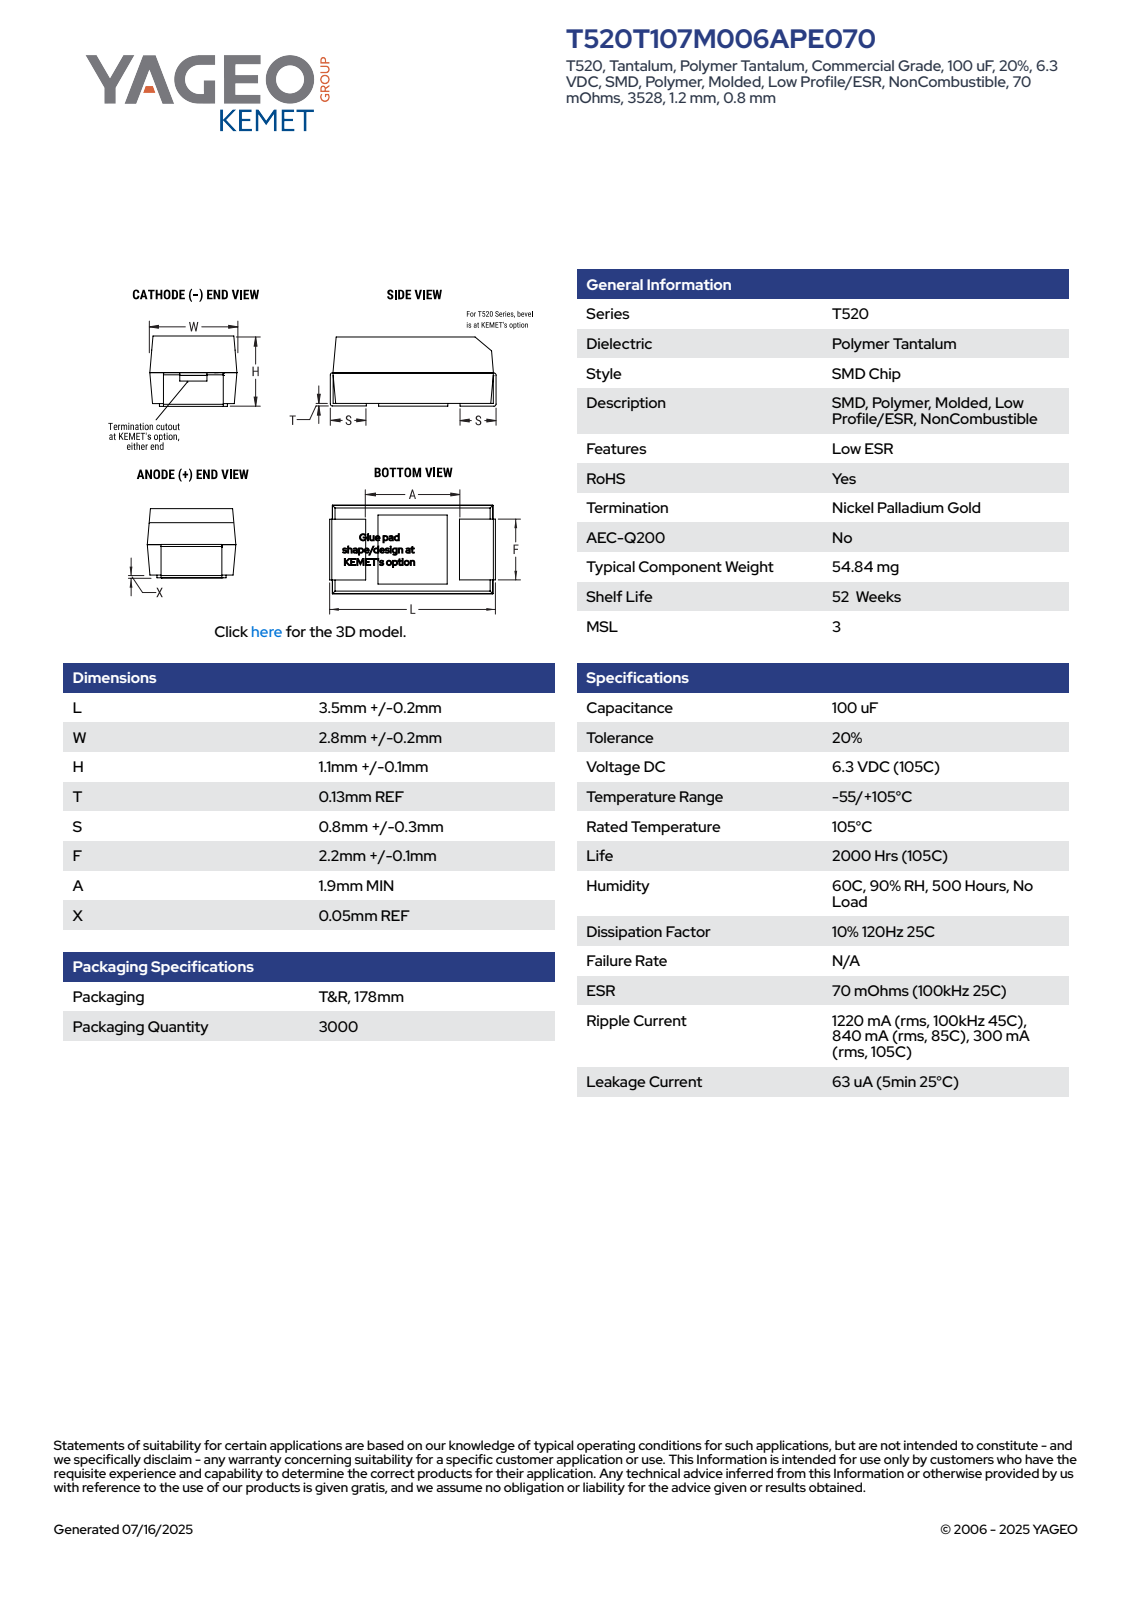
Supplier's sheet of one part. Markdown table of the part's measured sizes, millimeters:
| quantity | value |
| --- | --- |
| part name | CTS_TCM2NOBNOKBOPT_3528_L3.7W3H1.2T0.13S0.8F2.3A1.9X0.05 |
| STEP written by | SolidWorks 2014 (AUTOMOTIVE_DESIGN) |
| units | millimeters |
| bodies | 4 solids, 90 faces (86 planar, 4 cylindrical, 0 other) |
| overall size | 3.7 × 3 × 1.21 |
| volume | 11 mm³ |
| surface area | 41 mm² |
| partial cylindrical surfaces (radius × count) | 0.13 × 4 |
| main face-to-face distances | 1.12, 2.95, 3.38, 1.2, 1.07, 3.57, 3.44, 3.7, 0.8, 2.9 |
